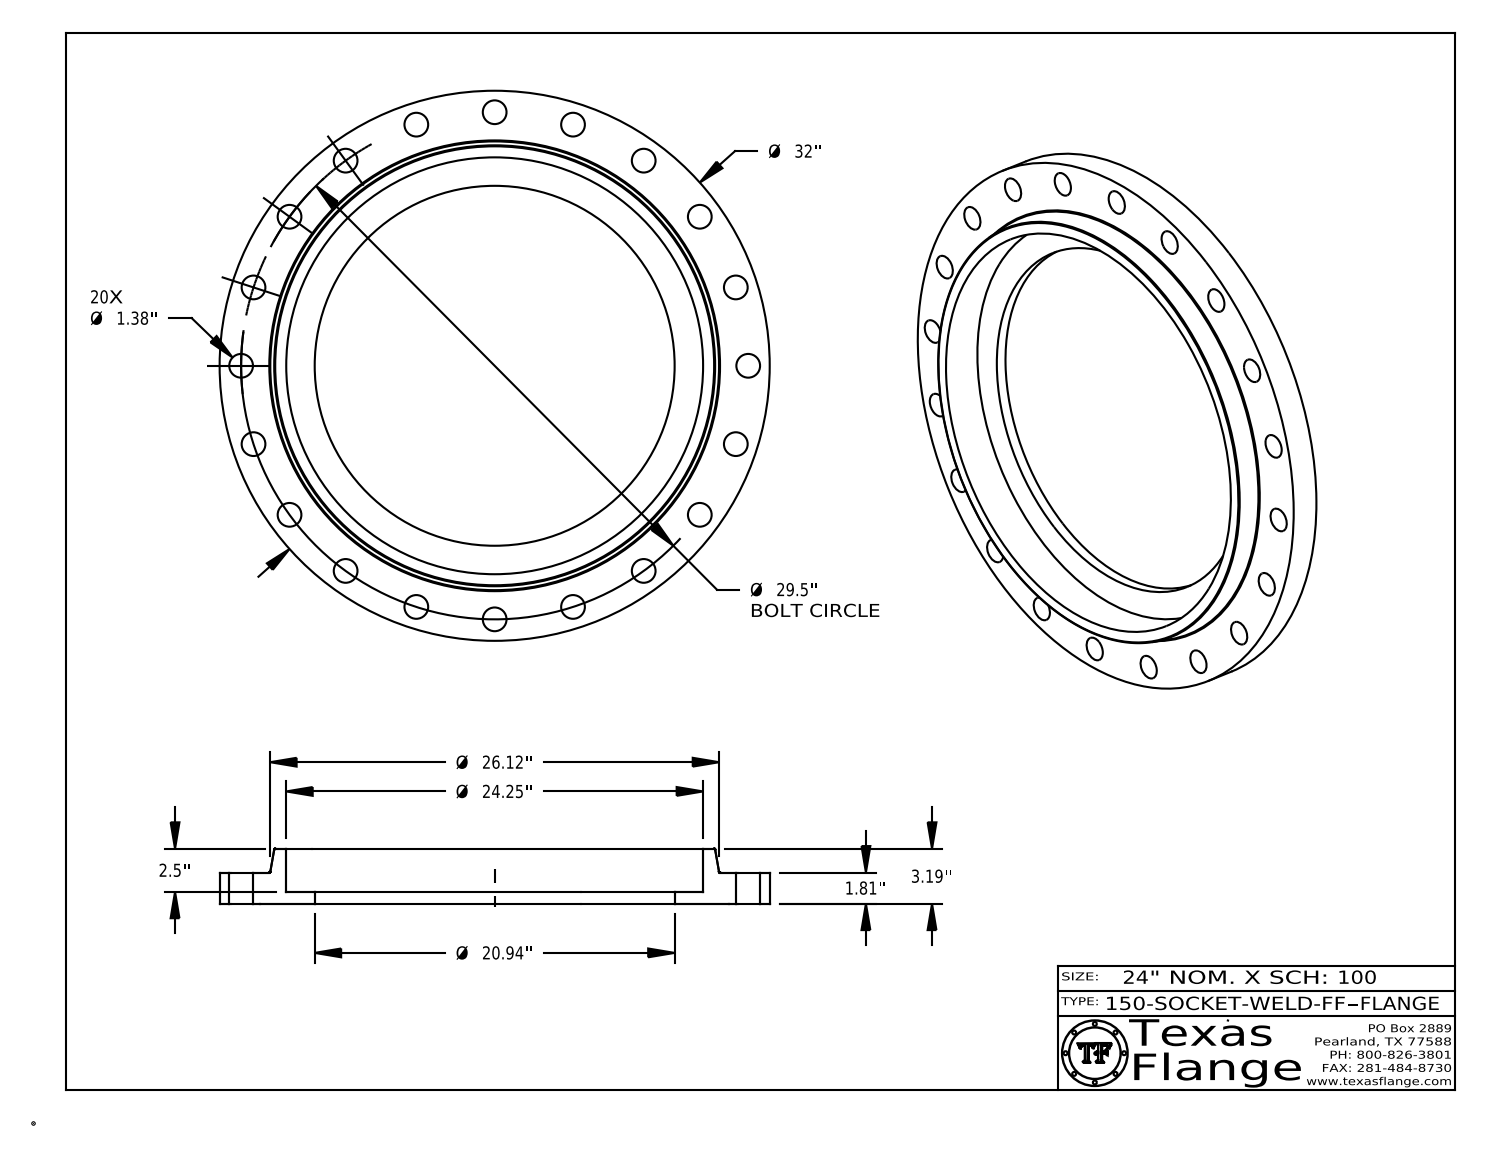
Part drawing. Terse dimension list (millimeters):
name: 150-SOCKET-WELD-FF
written by: CATIA V5 STEP AP214 (AUTOMOTIVE_DESIGN)
unit: mm
bodies: 1 solid, 442 faces (370 planar, 66 cylindrical, 6 other)
size: 812.8 × 812.8 × 81
volume: 12 050 000 mm³; area: 984 500 mm²
holes: 20× ⌀35.1, 1× ⌀12.6, 1× ⌀531.8, 1× ⌀616
bosses: 8× ⌀0.8, 1× ⌀812.8, 1× ⌀9.9
face distances: 46, 17.5, 28.4, 81, 63.5, 35.1, 45.6, 28.1, 0.4, 35.4
hole spacings: 374.7, 740.1, 117.2, 440.4, 529.8, 606.2, 667.6, 231.5
